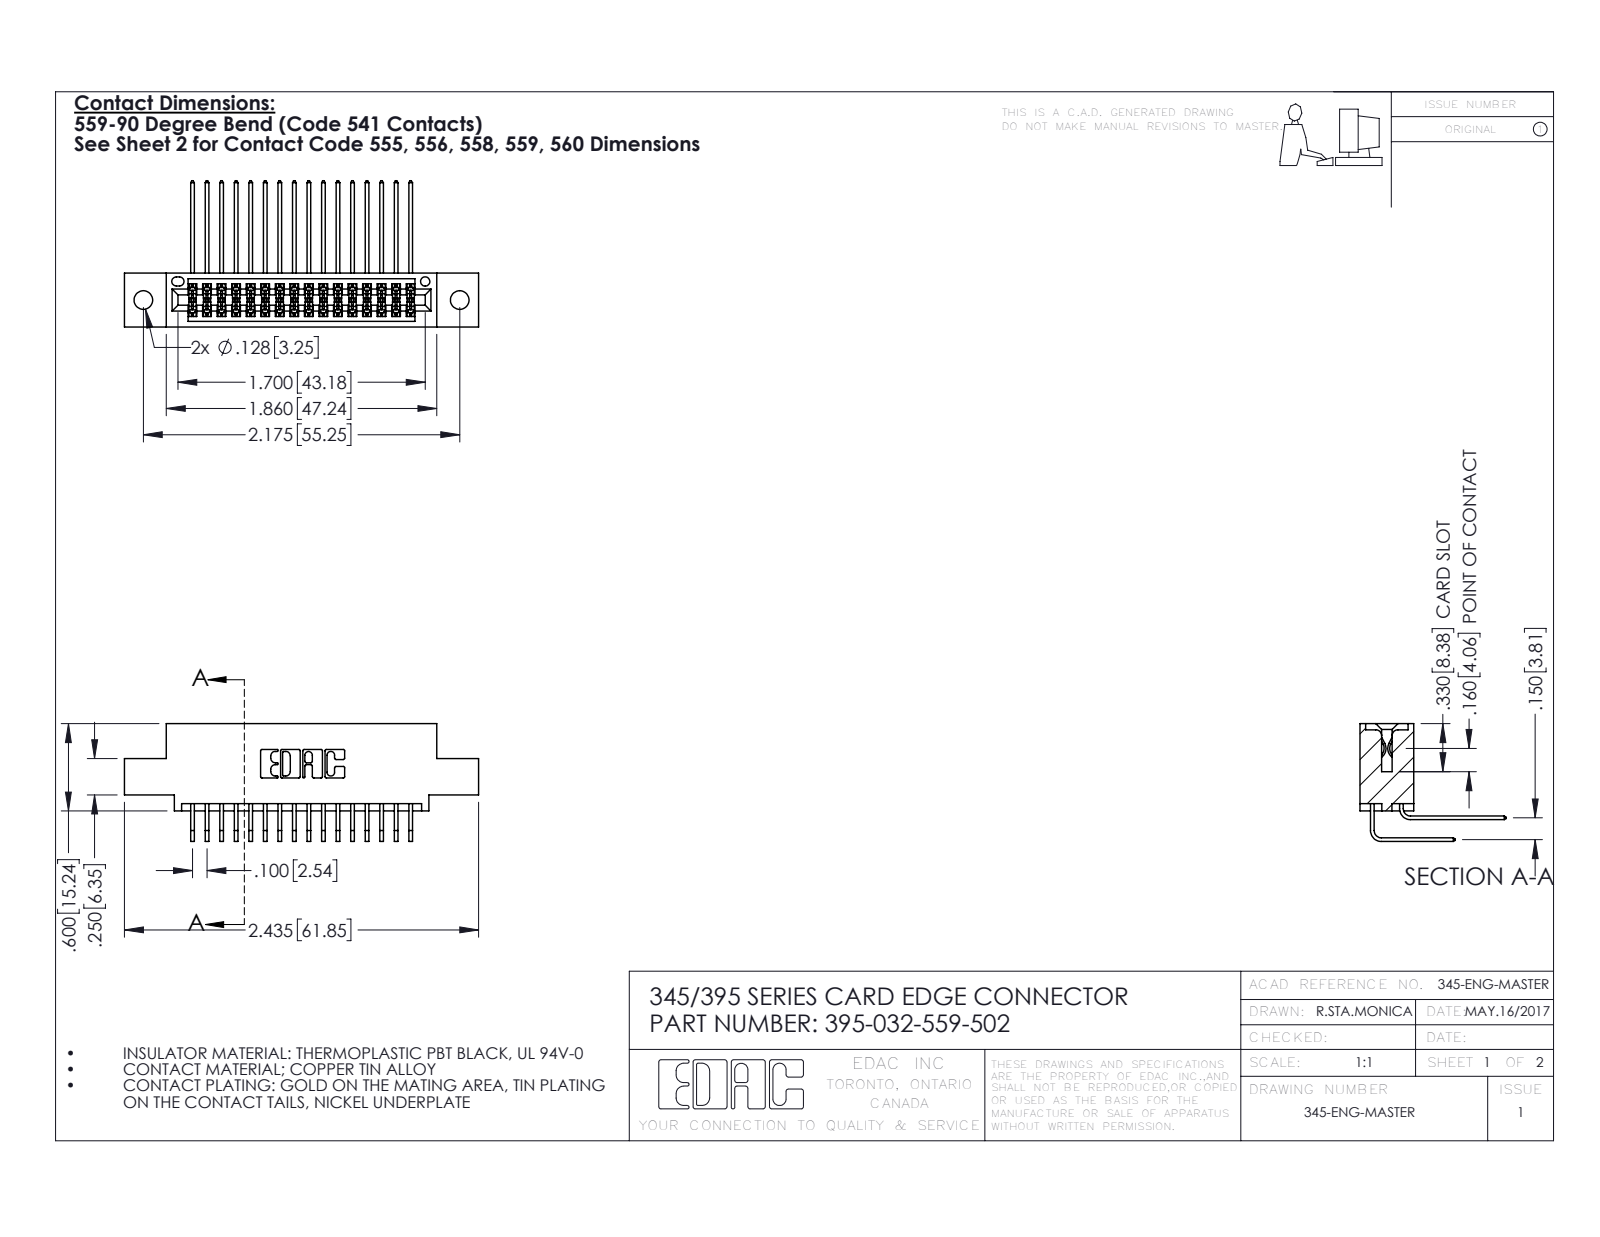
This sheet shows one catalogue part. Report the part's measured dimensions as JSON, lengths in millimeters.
{"part_name": "345 Part_0.110 Offset - 0.128 Dia; 345-292-001_558 559 Tail - 1; 395-032-559-502; 345-292-001_559 Tail - 2", "step_written_by": "SolidWorks 2016 (CONFIG_CONTROL_DESIGN)", "units": "millimeters", "bodies": {"solids": 33, "faces": 1794, "planar": 1204, "cylindrical": 590, "other": 0}, "overall_size": [61.8, 25.5, 20.5], "volume_mm3": 5830, "surface_area_mm2": 8819, "round_holes": [[3.3, 2], [1.6, 1]], "partial_cylinders_radius": [[0.2, 49], [0.3, 22], [0.2, 6], [0.8, 6], [0.7, 3], [0.4, 2], [0.5, 2], [0.6, 2]], "face_to_face_distances": [1.8, 7.6, 5.1, 9.4, 2.5, 6.9, 0.6, 5.7, 3.8, 4.4], "hole_center_spacings": [6.9, 49.3, 55.2]}
